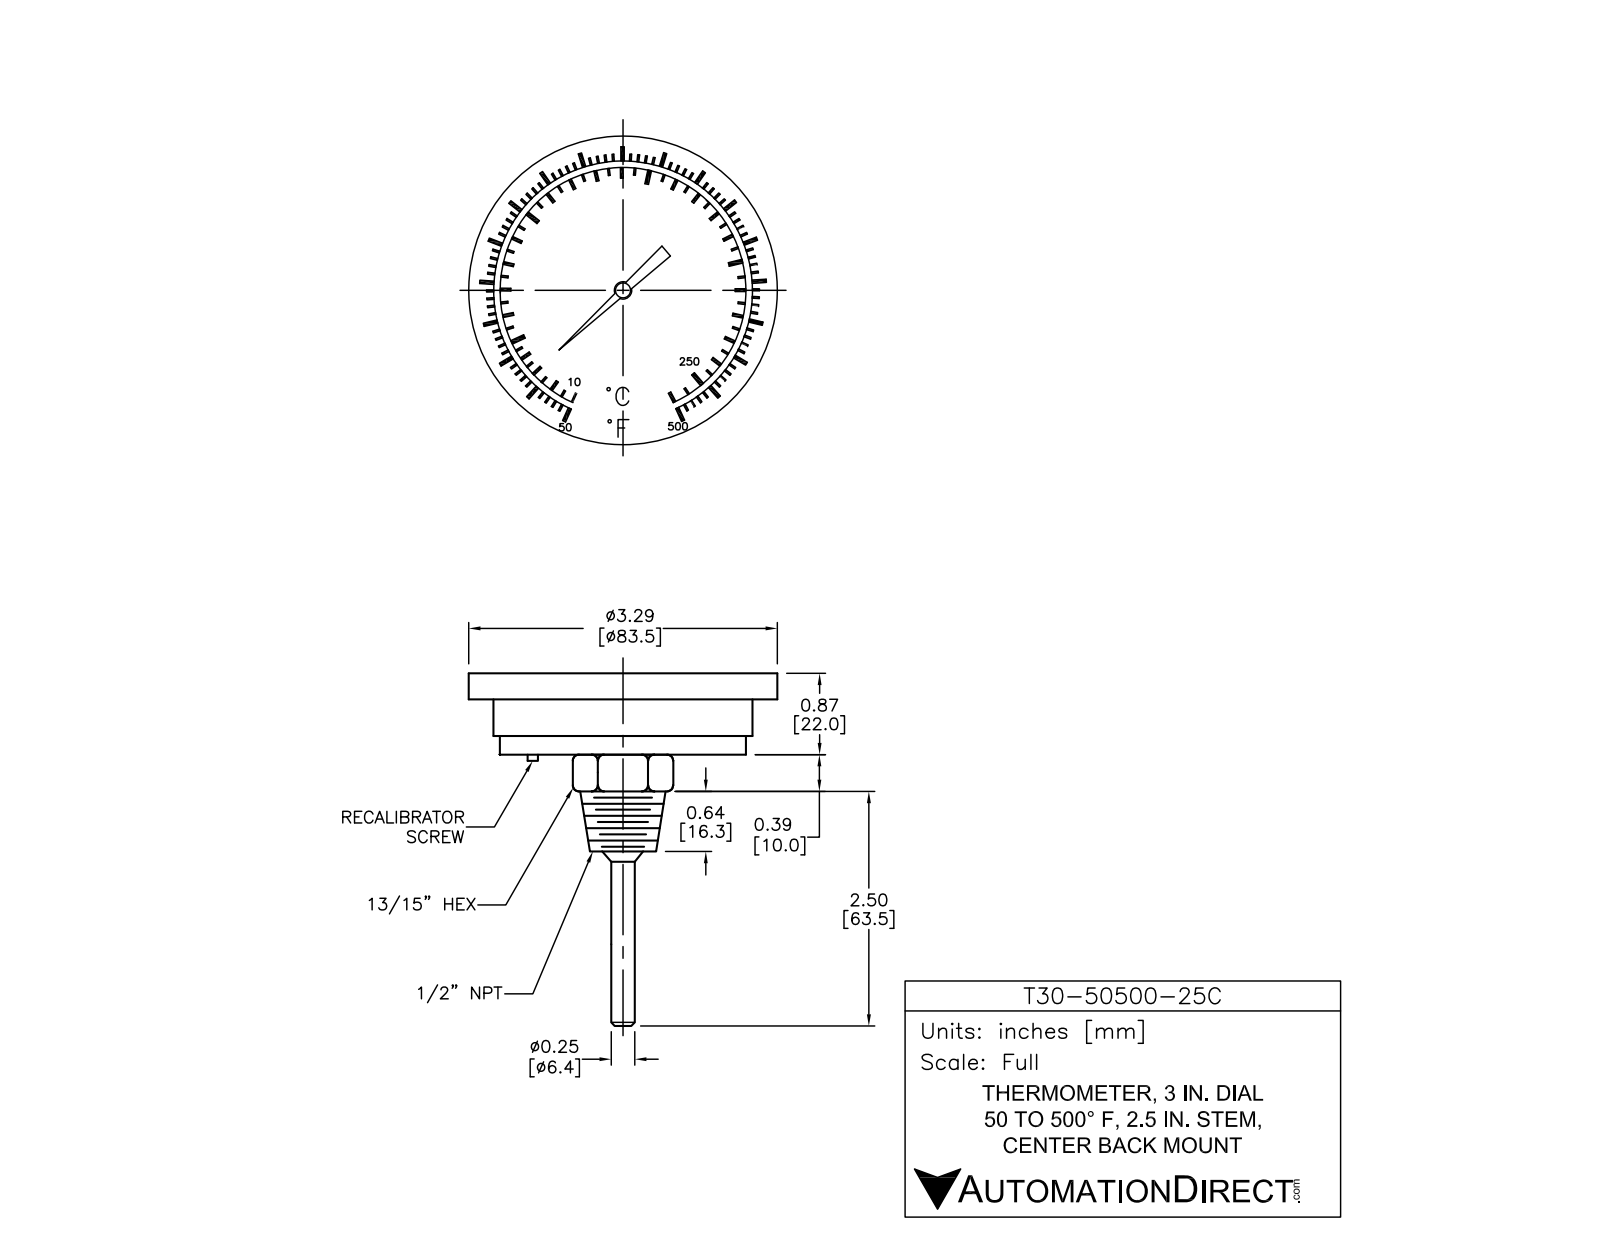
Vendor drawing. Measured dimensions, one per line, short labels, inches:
name: T30-50500-25C
written by: SolidWorks 2021 (AUTOMOTIVE_DESIGN)
unit: in
bodies: 57 solids, 934 faces (720 planar, 124 cylindrical, 90 other)
size: 5.26 × 3.29 × 3.29
volume: 3.15 in³; area: 34.08 in²
holes: 1× ⌀0.067, 1× ⌀2.69
bosses: 1× ⌀3.29, 1× ⌀2.76, 1× ⌀2.62, 1× ⌀0.845, 1× ⌀0.258
rounds: 1× R0.04, 1× R0.859, 1× R0.969
face distances: 0.222, 0.078, 0.3, 0.87, 0.648, 0.57, 0.29, 0.59, 0.368, 0.28
